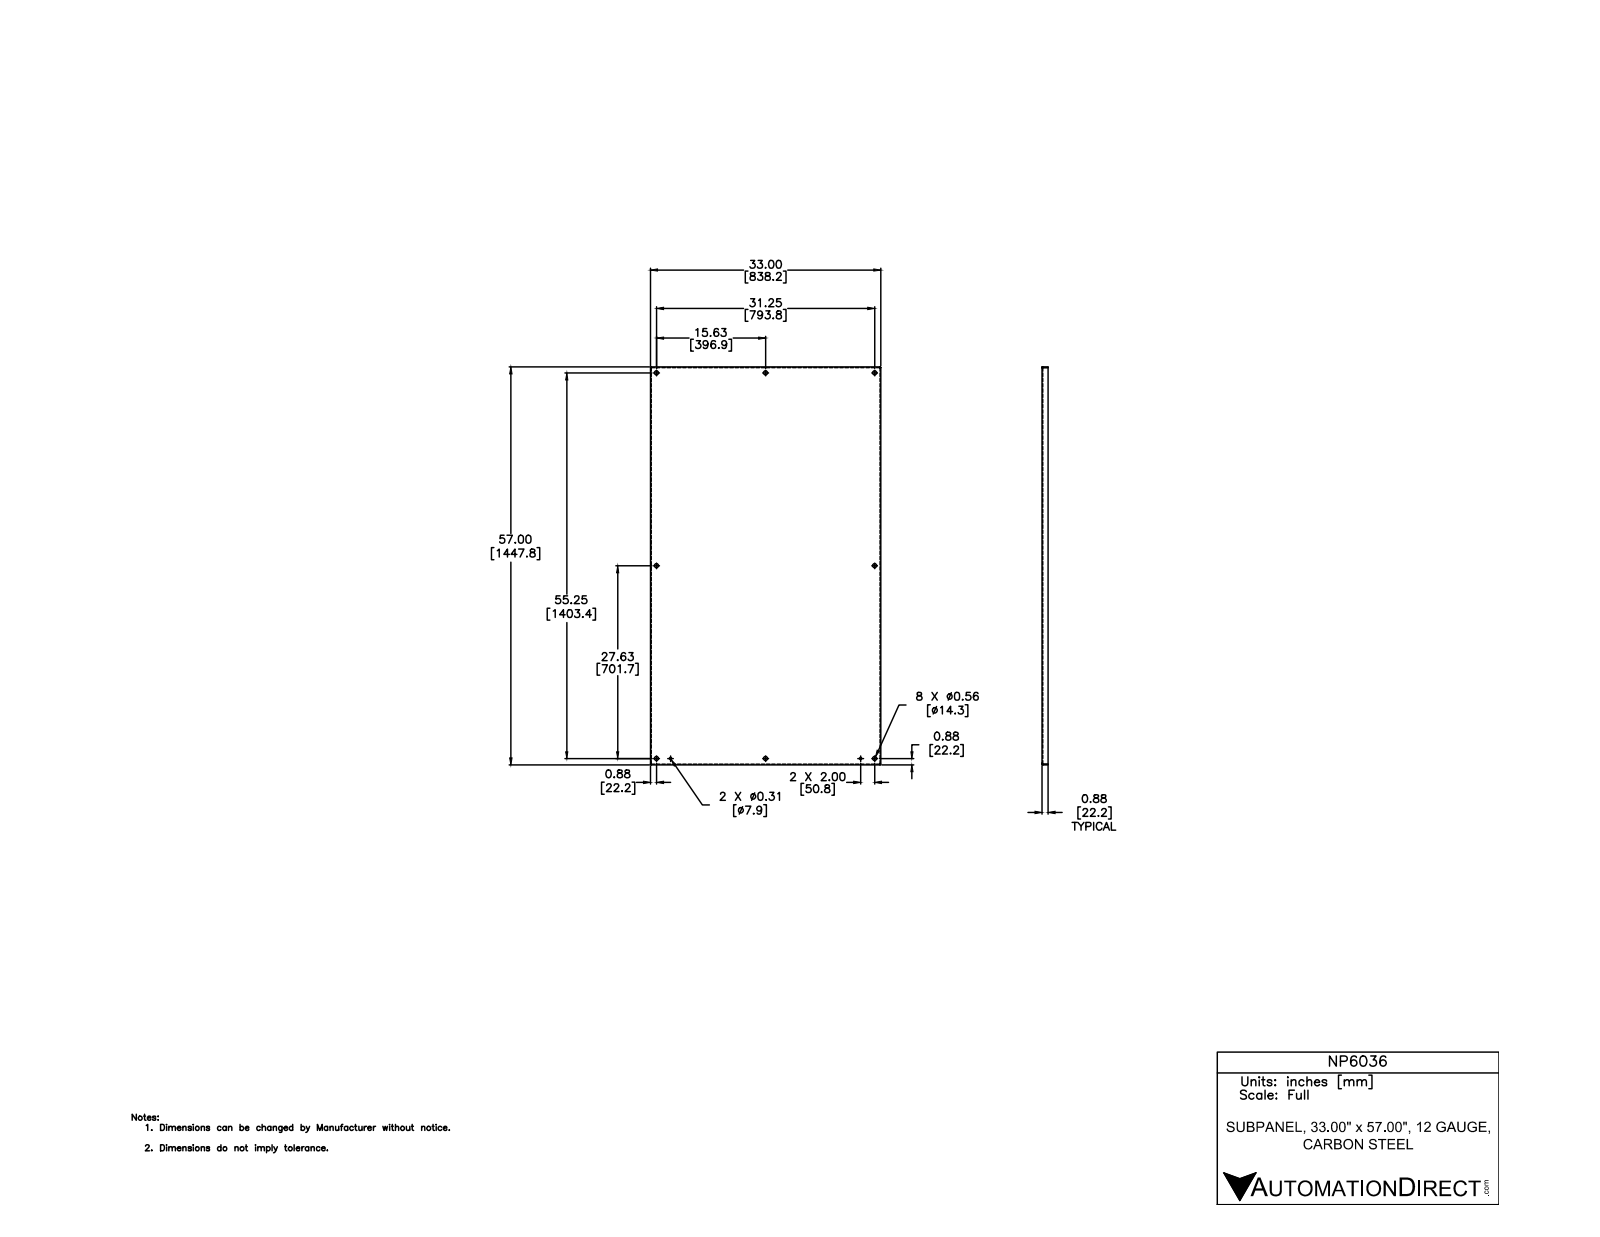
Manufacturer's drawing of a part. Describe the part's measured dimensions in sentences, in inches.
The part is named "NP6036". Its 3-D file was written by "Autodesk Inventor 2012 (AUTOMOTIVE_DESIGN)". It is 1 solid with 48 faces: 22 planar, 18 cylindrical and 8 other. Overall it measures 57 by 33 by 0.875 inches. Its volume is 188.7 cubic inches and its surface area 4 044 square inches. Round holes: 8 of diameter 0.563, 2 of diameter 0.312. Partial cylindrical surfaces (rounded edges, fillets, slot ends): 4 of radius 0.031, 4 of radius 0.125. The main face-to-face distances are 0.094, 32.906, 56.906, 33, 32.813, 56.813, 57, 0.781, 0.875, 0.105. The hole center spacings are 27.625, 31.738, 57.417, 55.25, 13.625, 15.625, 15.625, 27.698.
